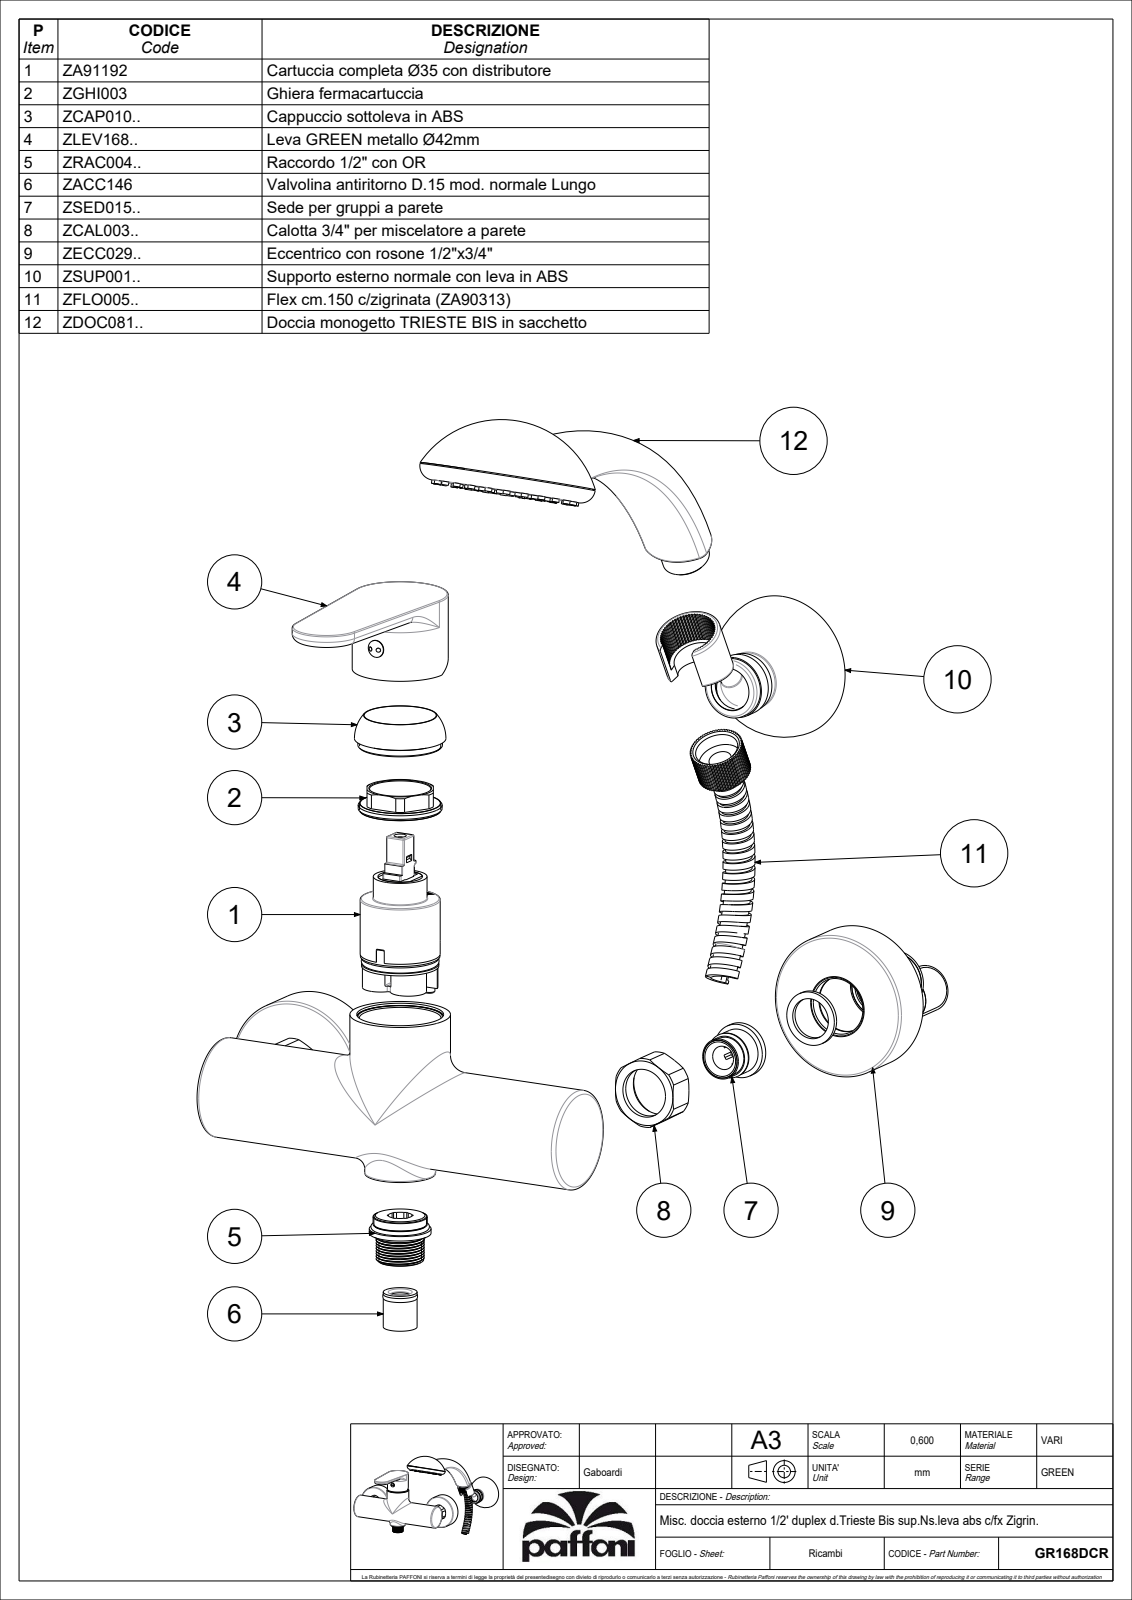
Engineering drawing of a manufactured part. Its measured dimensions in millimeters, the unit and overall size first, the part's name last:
Units: millimetres
Overall size (bounding box): 315.5 × 274.85 × 221.51
Round holes (diameter × count): ⌀1.5 ×48, ⌀19 ×4, ⌀5 ×3, ⌀7 ×2, ⌀10.5 ×2, ⌀15 ×2, ⌀16.5 ×2, ⌀20.5 ×2, ⌀21.5 ×2, ⌀24.1 ×2, ⌀25 ×2, ⌀26.7 ×2
Round bosses / shafts (diameter × count): ⌀3 ×48, ⌀27 ×4, ⌀24 ×4, ⌀26 ×3, ⌀63.5 ×2, ⌀44 ×2, ⌀26.4 ×2, ⌀21 ×2
Partial cylindrical surfaces — rounded edges, fillets, slot ends (radius × count): R0.5 ×2, R3 ×2, R10 ×2, R15.5 ×2, R4.5 ×1, R5.25 ×1, R11.75 ×1, R15 ×1
Main face-to-face distances: 0.6, 2.5, 27.5, 68.5, 6, 83, 112.5, 8.5, 3.25, 177.75
Hole centre spacings: 31, 8.09, 37.74, 53.69, 43.84, 57.28, 61.47, 49.19
Volume: 403 154 mm³ · Surface area: 199 338 mm²
Bodies: 23 solids, 1228 faces (450 planar, 504 cylindrical, 274 other)
Part name (STEP PRODUCT): 3021228TO; 2081068CR; 4061237CR; 2091105CR (+8 more)
STEP written by: CREO PARAMETRIC BY PTC INC, 2020044 (CONFIG_CONTROL_DESIGN)
